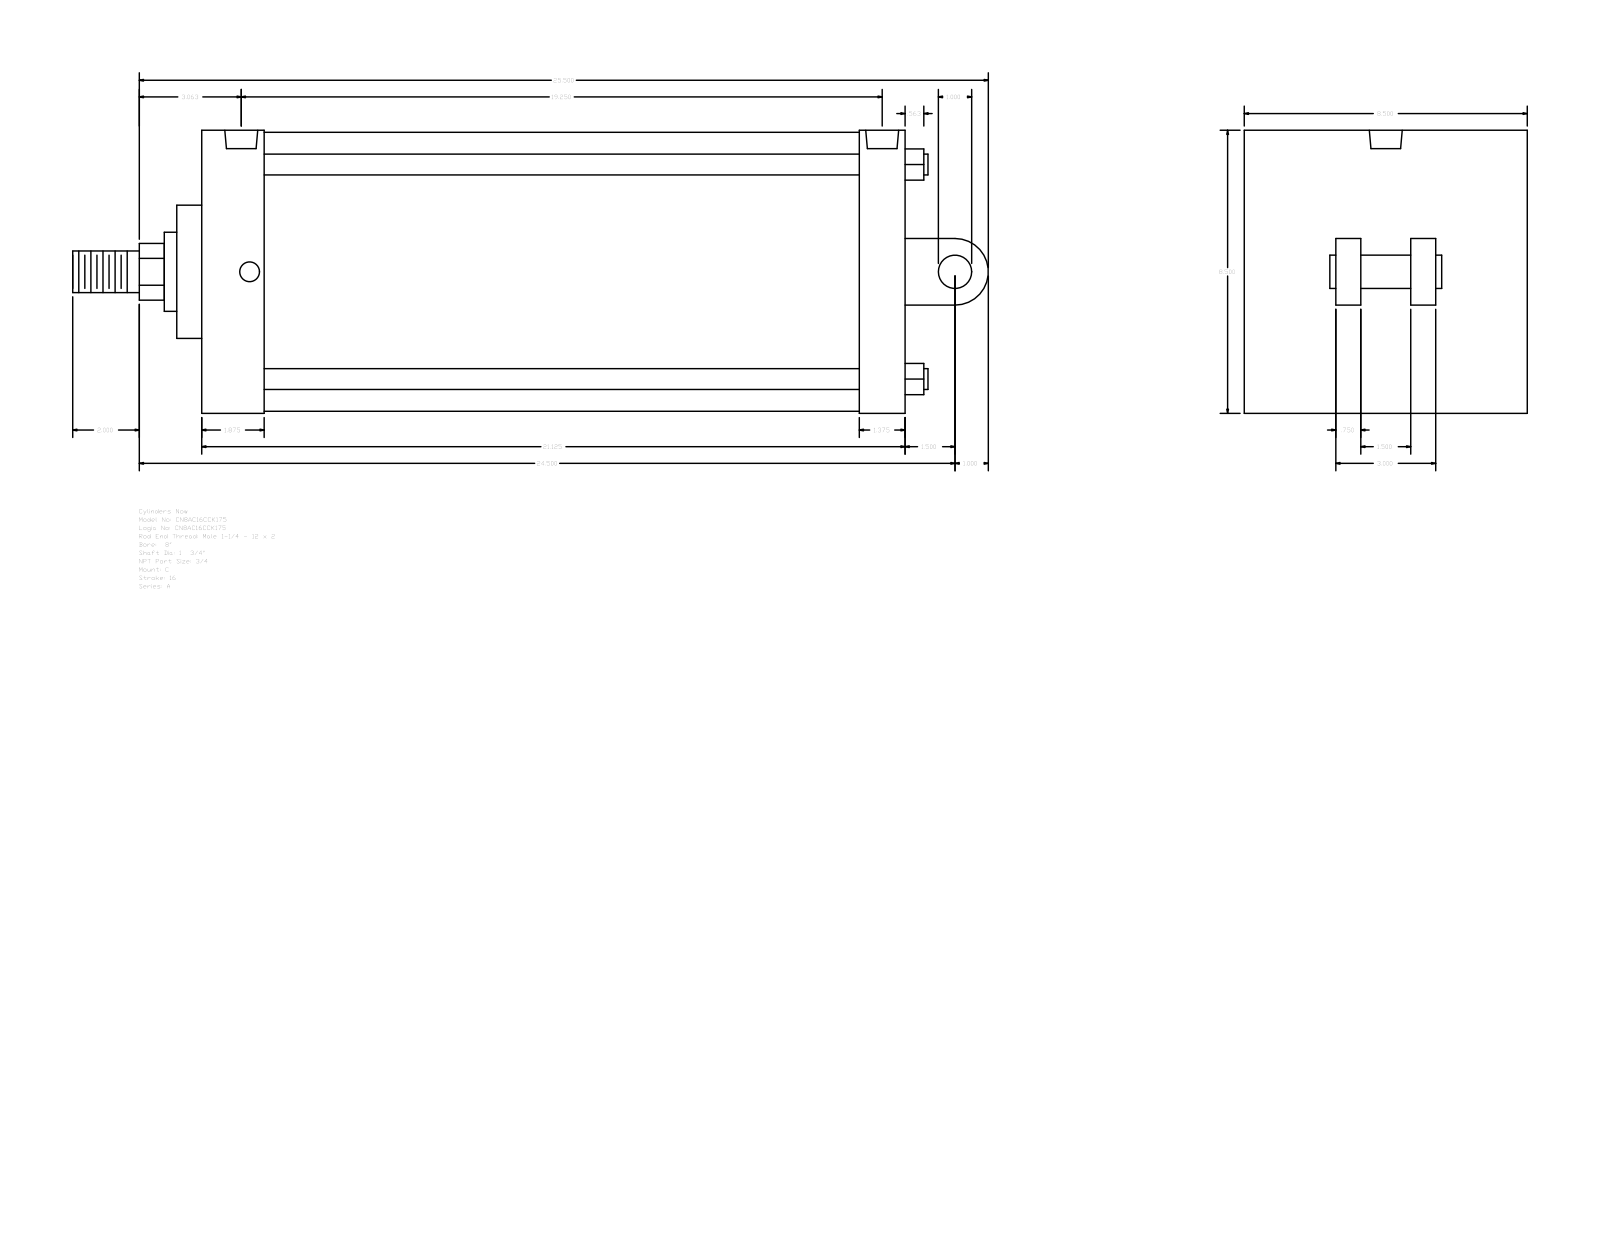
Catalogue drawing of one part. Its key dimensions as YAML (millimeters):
part_name: "A_C__0800_1.75"
step_written_by: "GSSL Pune (CONFIG_CONTROL_DESIGN)"
units: millimeters
bodies: {solids: 0, faces: 104, planar: 75, cylindrical: 29, other: 0}
overall_size: [698.5, 215.9, 215.9]
round_holes:
  - {diameter: 15.08, count: 4}
  - {diameter: 25.12, count: 2}
round_bosses_or_shafts:
  - {diameter: 15.88, count: 4}
  - {diameter: 212.72, count: 1}
  - {diameter: 60.33, count: 1}
  - {diameter: 44.45, count: 1}
  - {diameter: 31.75, count: 1}
  - {diameter: 25.4, count: 1}
partial_cylinders:
  - {radius: 21.63, count: 1}
  - {radius: 25.4, count: 1}
face_to_face_distances: [536.58, 215.9, 19.05, 57.15, 47.63, 488.95, 501.65, 454.02, 34.93, 69.85]
hole_center_spacings: [6.35, 476.25, 482.6, 488.95]
